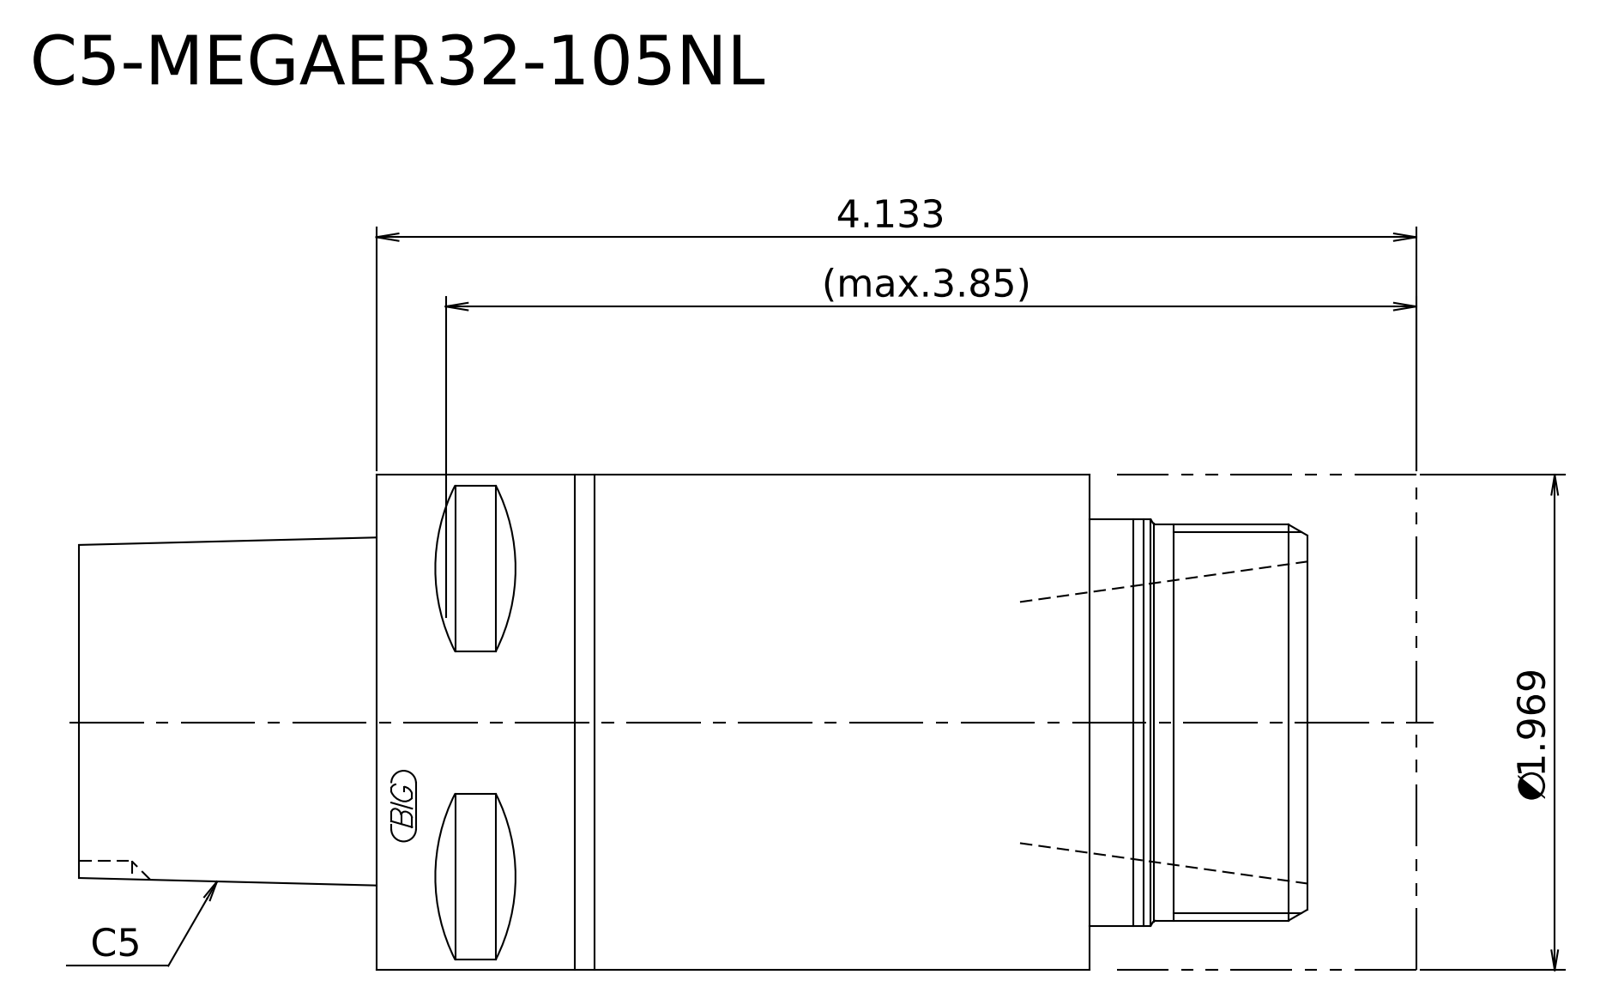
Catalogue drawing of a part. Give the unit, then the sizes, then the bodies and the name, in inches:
Units: inches
Overall size (bounding box): 5.315 × 1.969 × 1.969
Round bosses / shafts (diameter × count): ⌀1.969 ×1, ⌀1.614 ×1, ⌀1.575 ×1
Main face-to-face distances: 1.189, 0.433, 0.756, 4.134, 3.701, 2.945, 5.315, 4.882, 4.126, 1.181
Volume: 15.61 in³ · Surface area: 46.07 in²
Bodies: 2 solids, 13 faces (6 planar, 4 cylindrical, 3 other)
STEP written by: Kubotek KeyCreator 2011 V10.0.2 (22737) (automotive_design)
